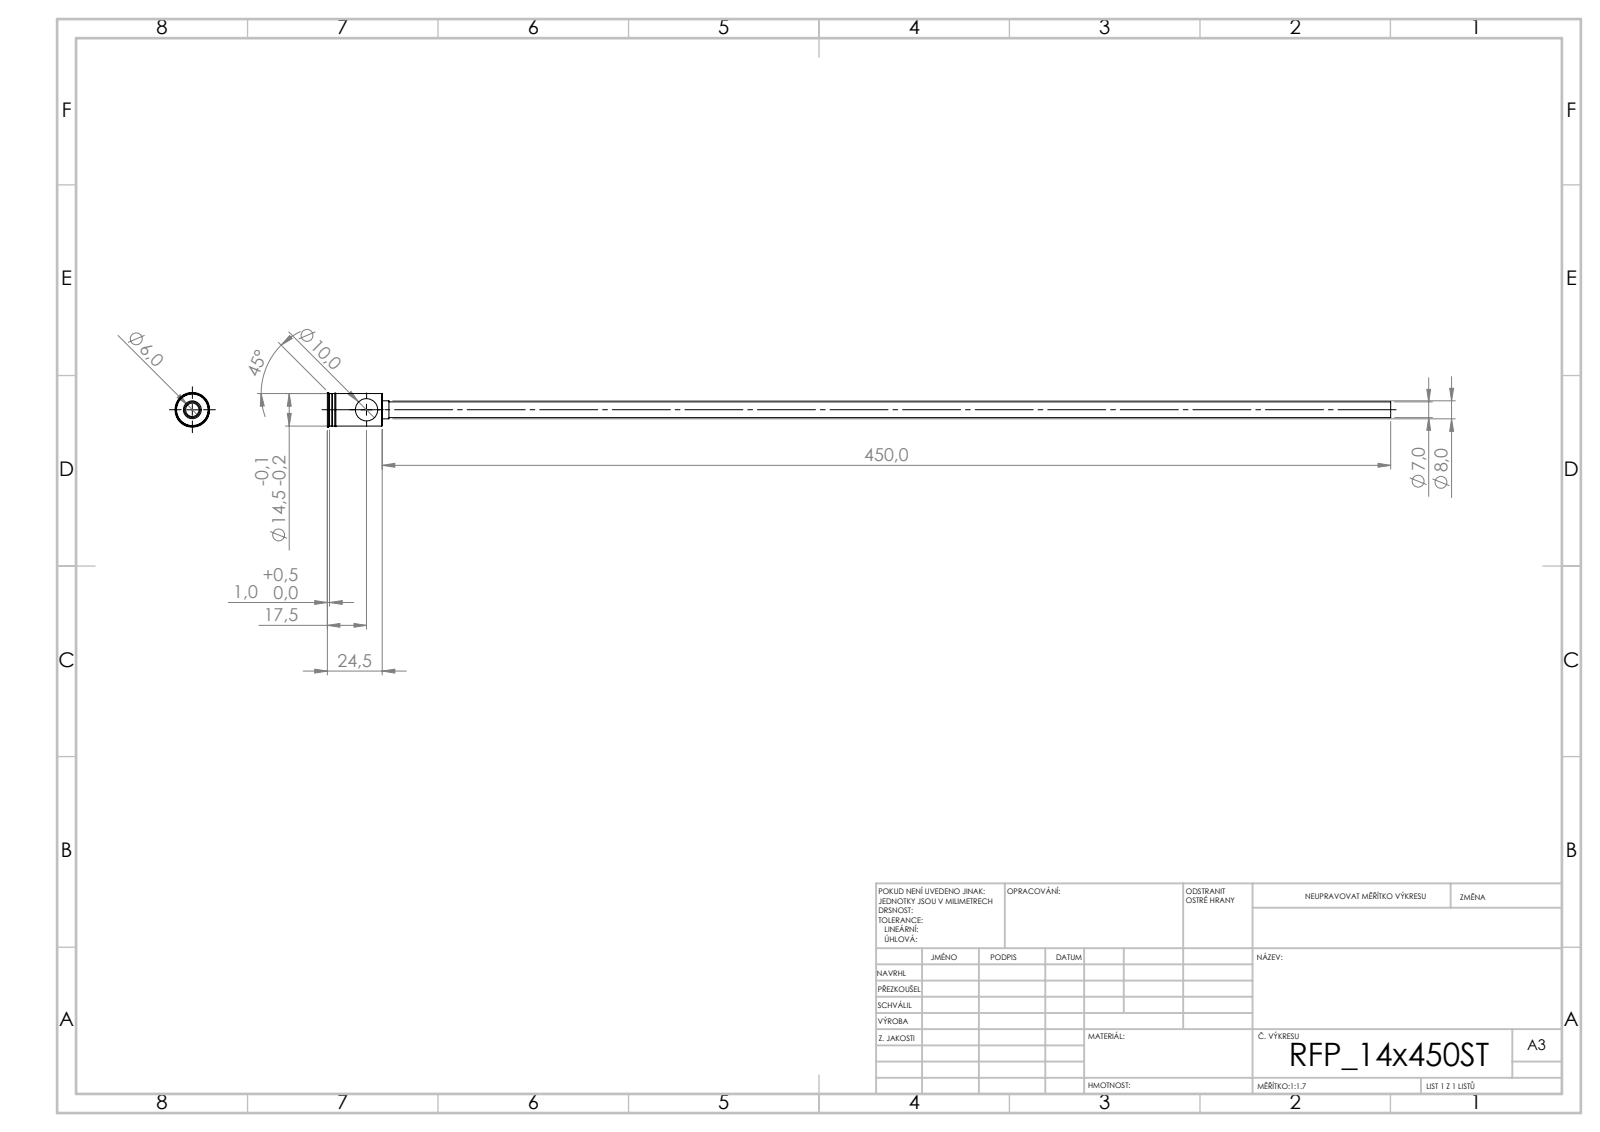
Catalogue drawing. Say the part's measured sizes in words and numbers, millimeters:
Its 3-D file was written by "SolidWorks 2019 (CONFIG_CONTROL_DESIGN)". It is 1 solid with 44 faces: 20 planar, 16 cylindrical and 8 other. Overall it measures 474.5 by 15.5 by 15.5 millimeters. Its volume is 7 396 cubic millimeters and its surface area 20 182 square millimeters. Round holes: 1 of diameter 6, 1 of diameter 10. Round bosses or shafts: 1 of diameter 15.5, 1 of diameter 14.5, 1 of diameter 8, 1 of diameter 7. The main face-to-face distances are 24.5, 22.5, 2, 9.9, 22.2, 2.3, 3, 25.2, 25.5, 27.5.
